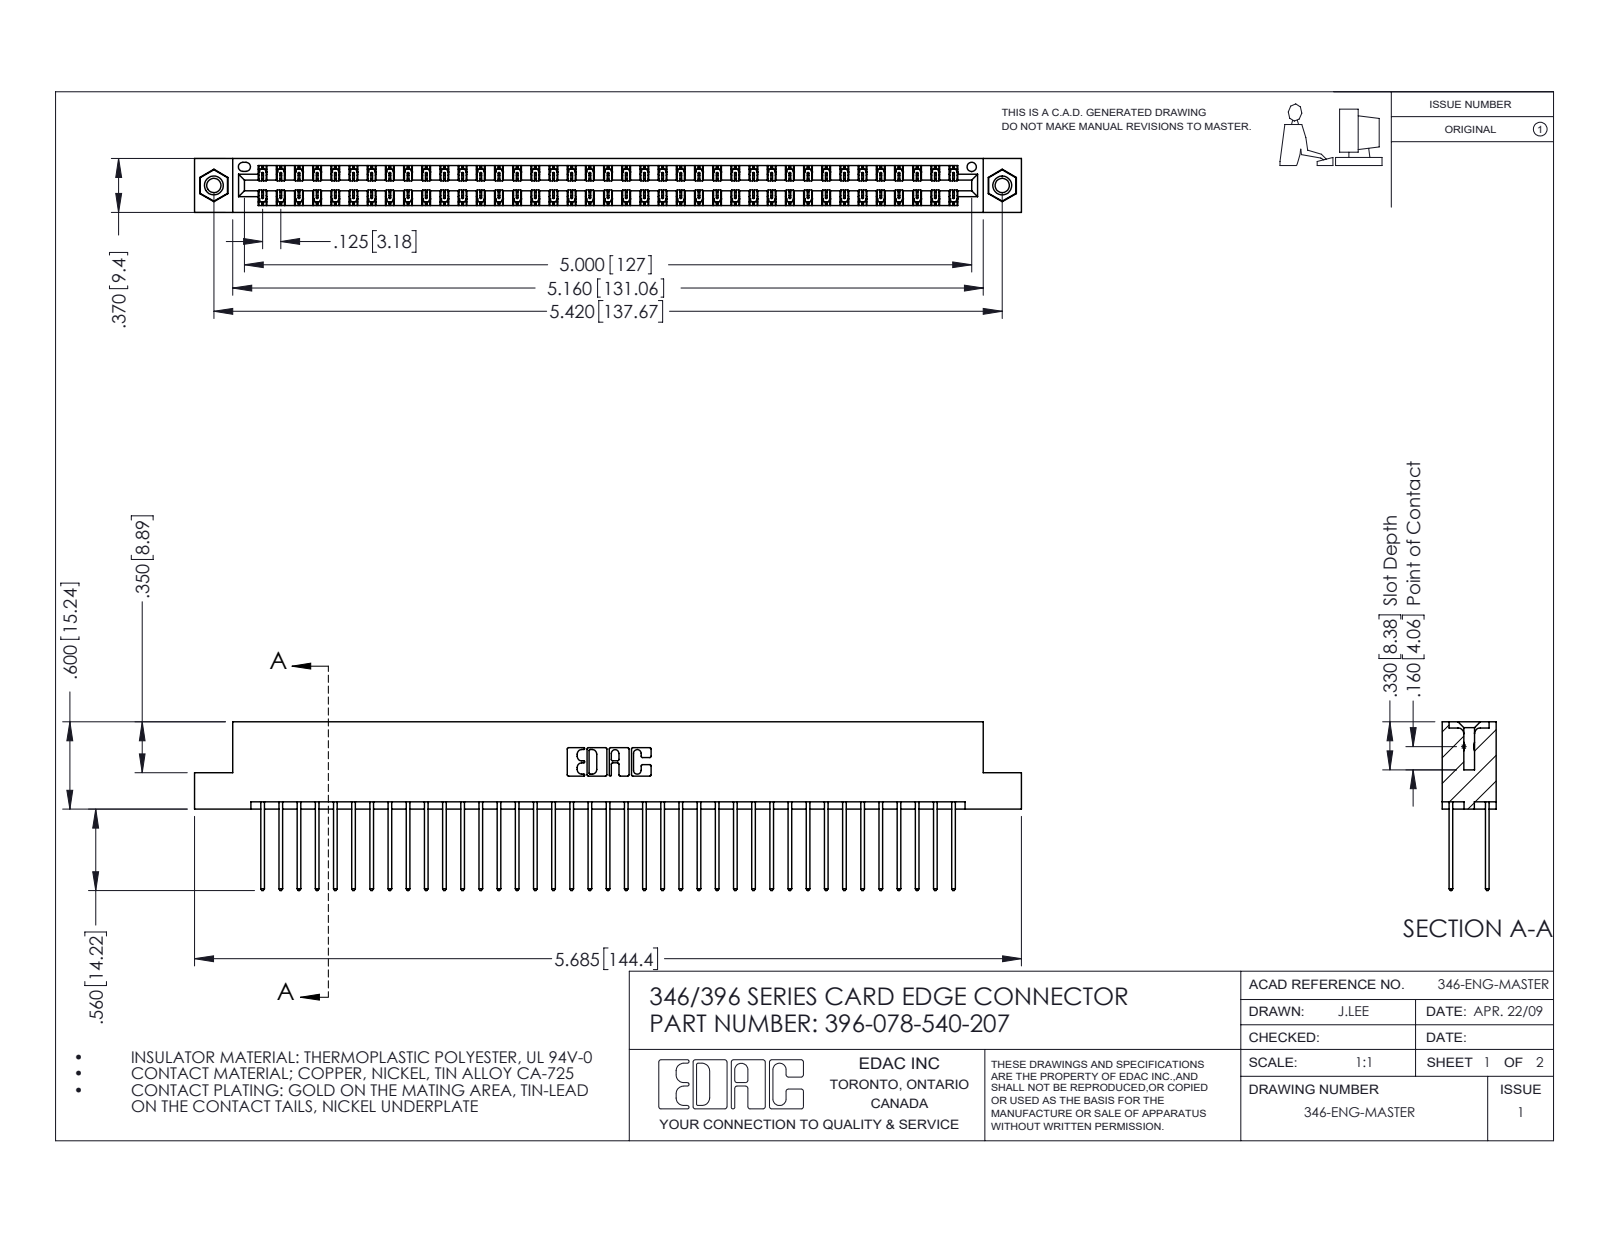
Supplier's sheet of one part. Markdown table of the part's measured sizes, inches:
| quantity | value |
| --- | --- |
| part name | 345-250-001_345-250-005-103; 346 Part_Flush Mounting Lugs - 0.156 Dia-TI; 345-292-001_345-293-140; 396-078-540-207 |
| STEP written by | SolidWorks 2016 (CONFIG_CONTROL_DESIGN) |
| units | inches |
| bodies | 81 solids, 4238 faces (2838 planar, 1384 cylindrical, 16 other) |
| overall size | 5.685 × 1.16 × 0.37 |
| volume | 0.875 in³ |
| surface area | 32.7 in² |
| round holes (diameter × count) | 0.098 × 2, 0.125 × 2, 0.156 × 2, 0.064 × 1 |
| round bosses / shafts (diameter × count) | 0.155 × 2 |
| partial cylindrical surfaces (radius × count) | 0.006 × 117, 0.01 × 78, 0.01 × 22, 0.007 × 6, 0.031 × 6, 0.026 × 3, 0.014 × 2, 0.022 × 2 |
| main face-to-face distances | 0.048, 0.322, 0.25, 0.072, 0.298, 0.025, 0.37, 0.275, 0.148, 0.222 |
| hole center spacings | 0.246, 5.211, 5.42 |
